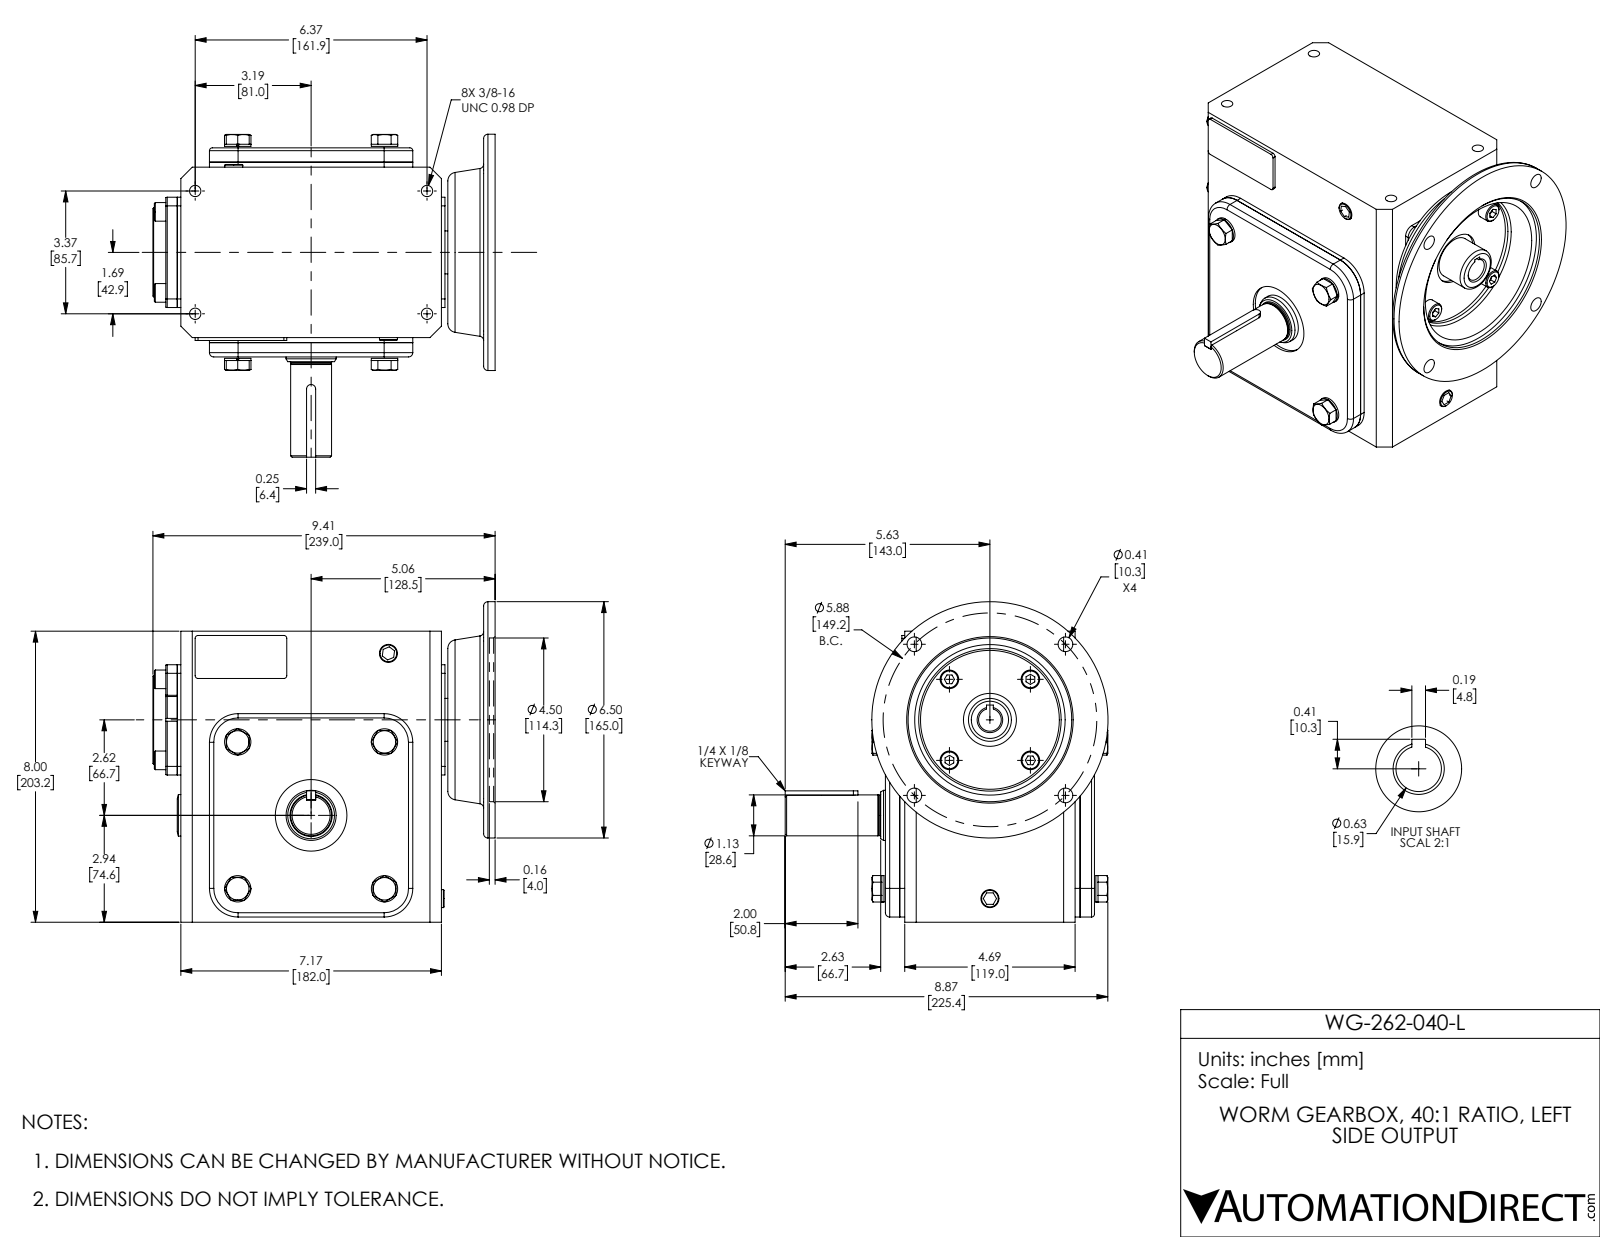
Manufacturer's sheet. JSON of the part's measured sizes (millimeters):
{"part_name": "WG-262-040-L", "step_written_by": "SolidWorks 2017 (AUTOMOTIVE_DESIGN)", "units": "millimeters", "bodies": {"solids": 37, "faces": 536, "planar": 293, "cylindrical": 145, "other": 98}, "overall_size": [239, 225.5, 223.8], "volume_mm3": 5213000, "surface_area_mm2": 395900, "round_holes": [[8, 4], [10.3, 4], [15, 1], [15.9, 1], [30, 1], [35, 1], [37, 1], [50, 1], [97, 1], [114.3, 1]], "round_bosses_or_shafts": [[18.4, 4], [13, 4], [165, 1], [62, 1], [52, 1], [29, 1], [28.6, 1], [28.3, 1]], "partial_cylinders_radius": [[2, 12], [3, 4], [6, 4], [20, 4], [0.5, 2], [1, 2], [3.2, 1]], "face_to_face_distances": [10, 126, 136, 13.5, 132.5, 3.5, 122.5, 203.2, 2.5, 184.5], "hole_center_spacings": [74.6, 105.5, 54.6, 85.7, 130.6, 149.2, 161.9, 183.2]}
